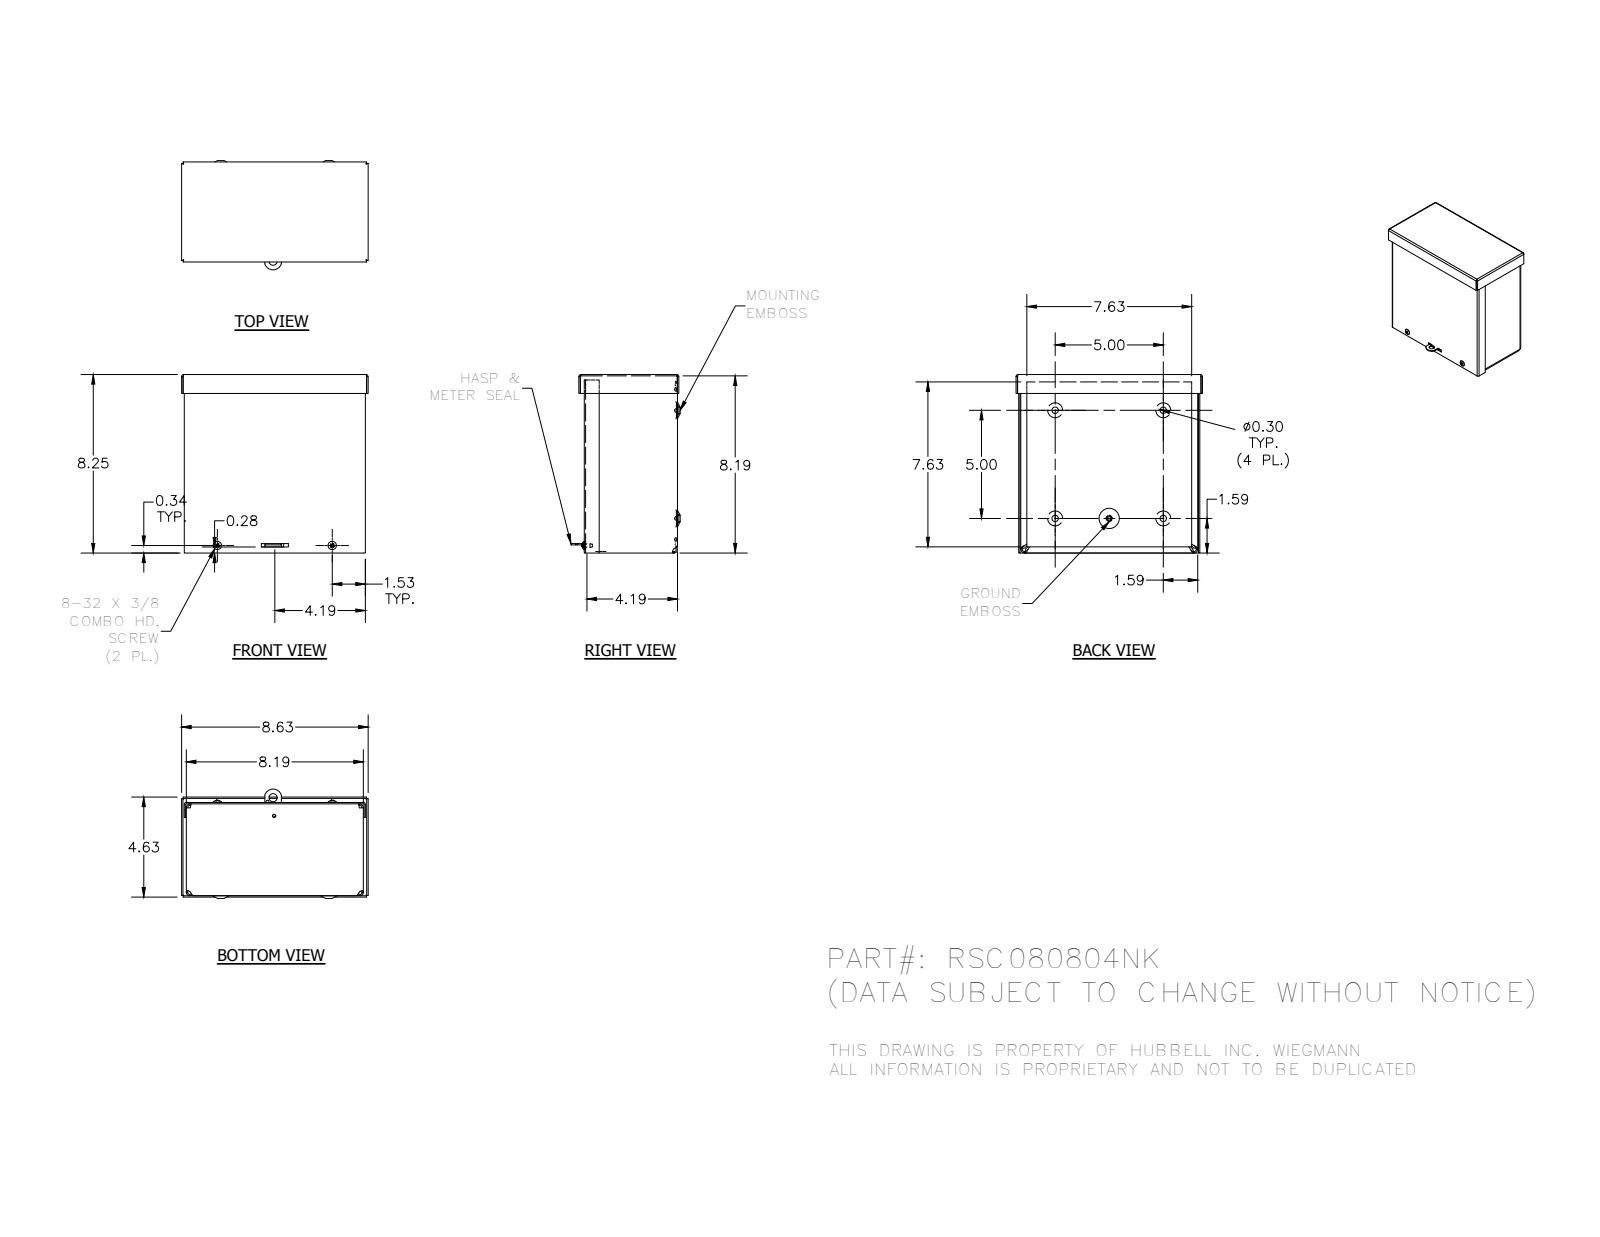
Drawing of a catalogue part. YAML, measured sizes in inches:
part_name: "RSC080804NK_WRAP; RSC0808NK_LID; RSC0804NK_CAP; 3183 (+3 more)"
step_written_by: "Autodesk Inventor 2014 (AUTOMOTIVE_DESIGN)"
units: inches
bodies: {solids: 7, faces: 377, planar: 163, cylindrical: 78, other: 136}
overall_size: [8.625, 8.25, 5.125]
volume: 23.22
surface_area: 761.5
round_holes:
  - {diameter: 0.3, count: 4}
  - {diameter: 0.313, count: 4}
  - {diameter: 0.148, count: 2}
  - {diameter: 0.125, count: 1}
  - {diameter: 0.136, count: 1}
  - {diameter: 0.156, count: 1}
  - {diameter: 0.165, count: 1}
  - {diameter: 0.375, count: 1}
round_bosses_or_shafts:
  - {diameter: 0.384, count: 2}
  - {diameter: 0.164, count: 2}
  - {diameter: 0.228, count: 1}
partial_cylinders:
  - {radius: 0.031, count: 8}
  - {radius: 0.093, count: 8}
  - {radius: 0.125, count: 8}
  - {radius: 0.187, count: 8}
  - {radius: 0.055, count: 4}
  - {radius: 0.062, count: 4}
  - {radius: 0.094, count: 4}
  - {radius: 0.117, count: 4}
face_to_face_distances: [0.062, 8.126, 0.062, 4.249, 4.187, 8.188, 0.063, 0.124, 4.312, 4.25]
hole_center_spacings: [5, 1.072, 1.261, 2.5, 5.313, 5.59, 6.063, 6.253]
